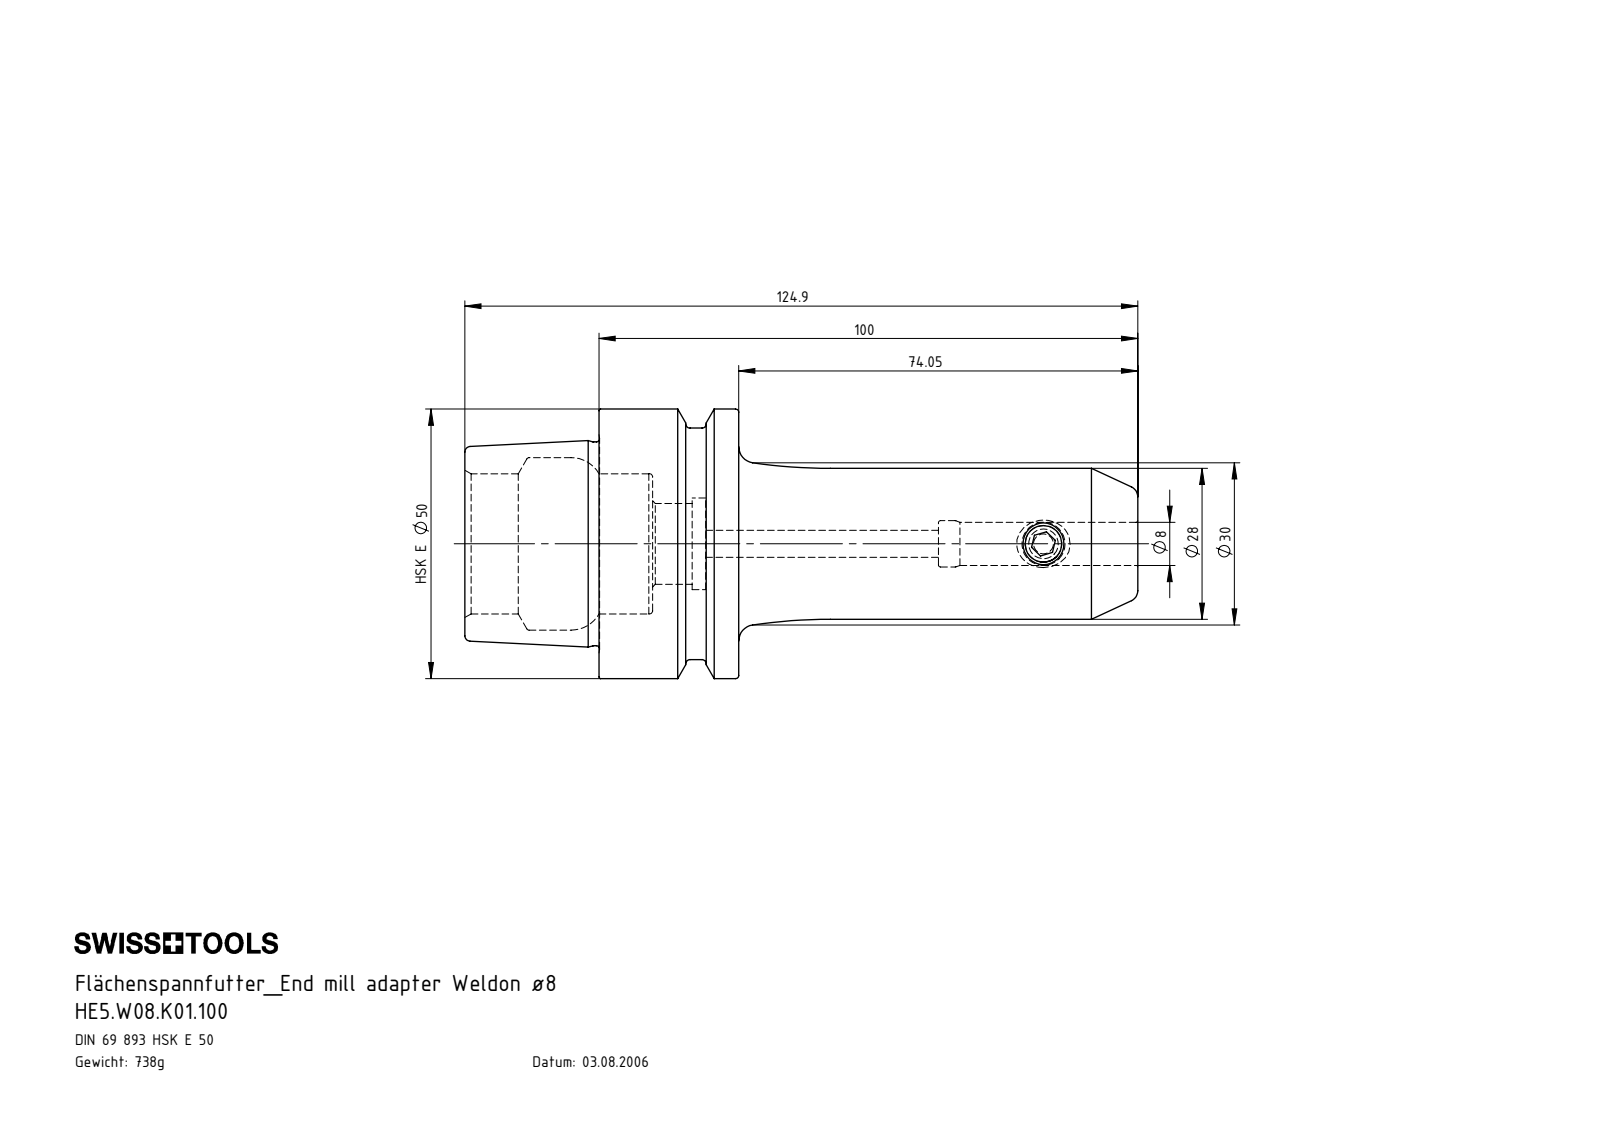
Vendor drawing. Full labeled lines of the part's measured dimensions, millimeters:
Part name (STEP PRODUCT): W08-ER1.001.010; HE5.W08.K01.100; HE5-W08.K01.100_B_Fertigbearbeitung
STEP written by: SolidWorks 2017 (AUTOMOTIVE_DESIGN)
Units: millimetres
Bodies: 2 solids, 111 faces (19 planar, 30 cylindrical, 62 other)
Overall size (bounding box): 124.9 × 50 × 50
Volume: 94 008 mm³ · Surface area: 23 181 mm²
Round holes (diameter × count): ⌀5 ×1, ⌀6.8 ×1, ⌀8 ×1, ⌀8.6 ×1, ⌀15 ×1, ⌀17 ×1, ⌀26 ×1, ⌀32 ×1
Round bosses / shafts (diameter × count): ⌀50 ×1, ⌀42.95 ×1, ⌀37.81 ×1, ⌀28 ×1, ⌀8 ×1
Main face-to-face distances: 25.95, 24.9, 50.85, 34.85, 9.95, 16, 44.7, 19.8, 9.85, 6.15
